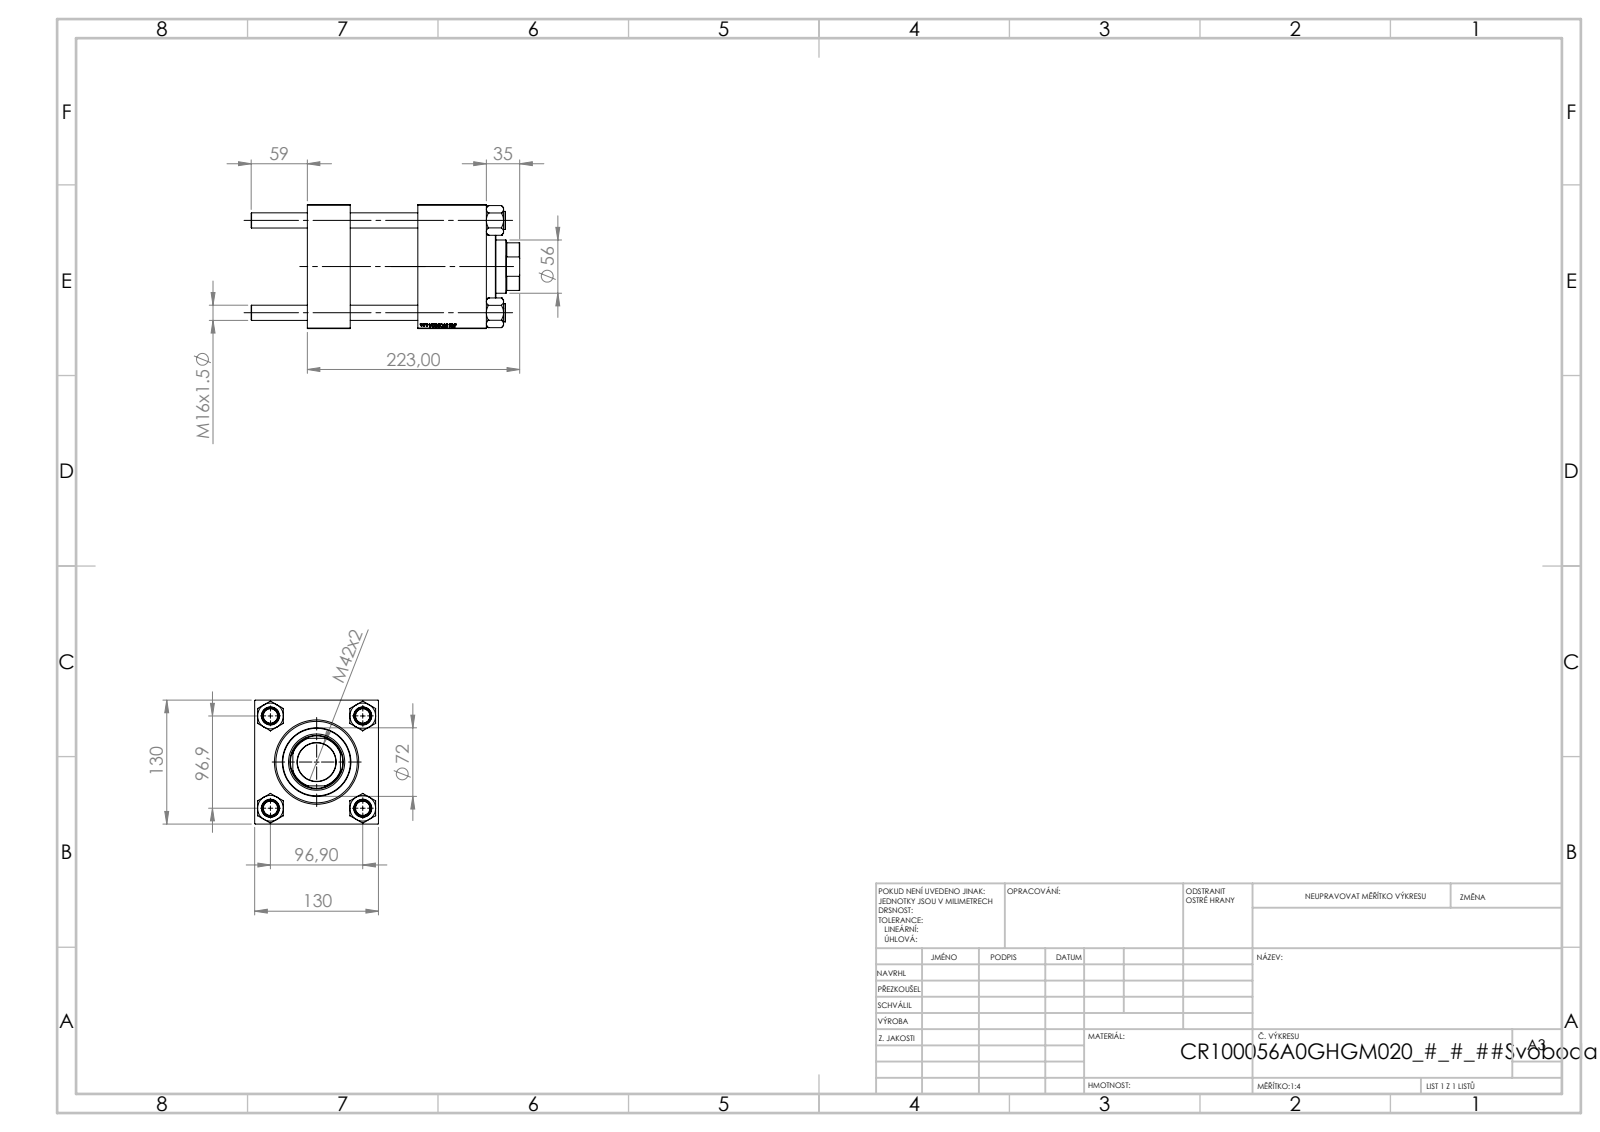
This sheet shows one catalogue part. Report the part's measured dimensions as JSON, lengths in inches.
{"part_name": "V215CR_BODY_A; NUT_M5; CR025_012_A_0_G_A_G_M_020_+#_##_TYCINKA; V215_VC_A (+1 more)", "step_written_by": "SolidWorks 2019 (CONFIG_CONTROL_DESIGN)", "units": "inches", "bodies": {"solids": 11, "faces": 1182, "planar": 568, "cylindrical": 78, "other": 536}, "overall_size": [11.102, 5.118, 5.118], "volume_in3": 155.9, "surface_area_in2": 558.9, "round_holes": [[0.63, 4], [0.276, 2], [1.041, 2], [1.378, 2], [1.594, 1], [2.205, 1], [2.323, 1], [2.992, 1], [3.366, 1], [3.937, 1]], "round_bosses_or_shafts": [[0.748, 4], [4.173, 1], [2.835, 1]], "partial_cylinders_radius": [[1.063, 1]], "face_to_face_distances": [5.118, 1.772, 7.402, 5.63, 4.567, 2.795, 2.835, 0.787, 3.622, 3.78], "hole_center_spacings": [2.698, 3.815, 5.395, 4.665]}
